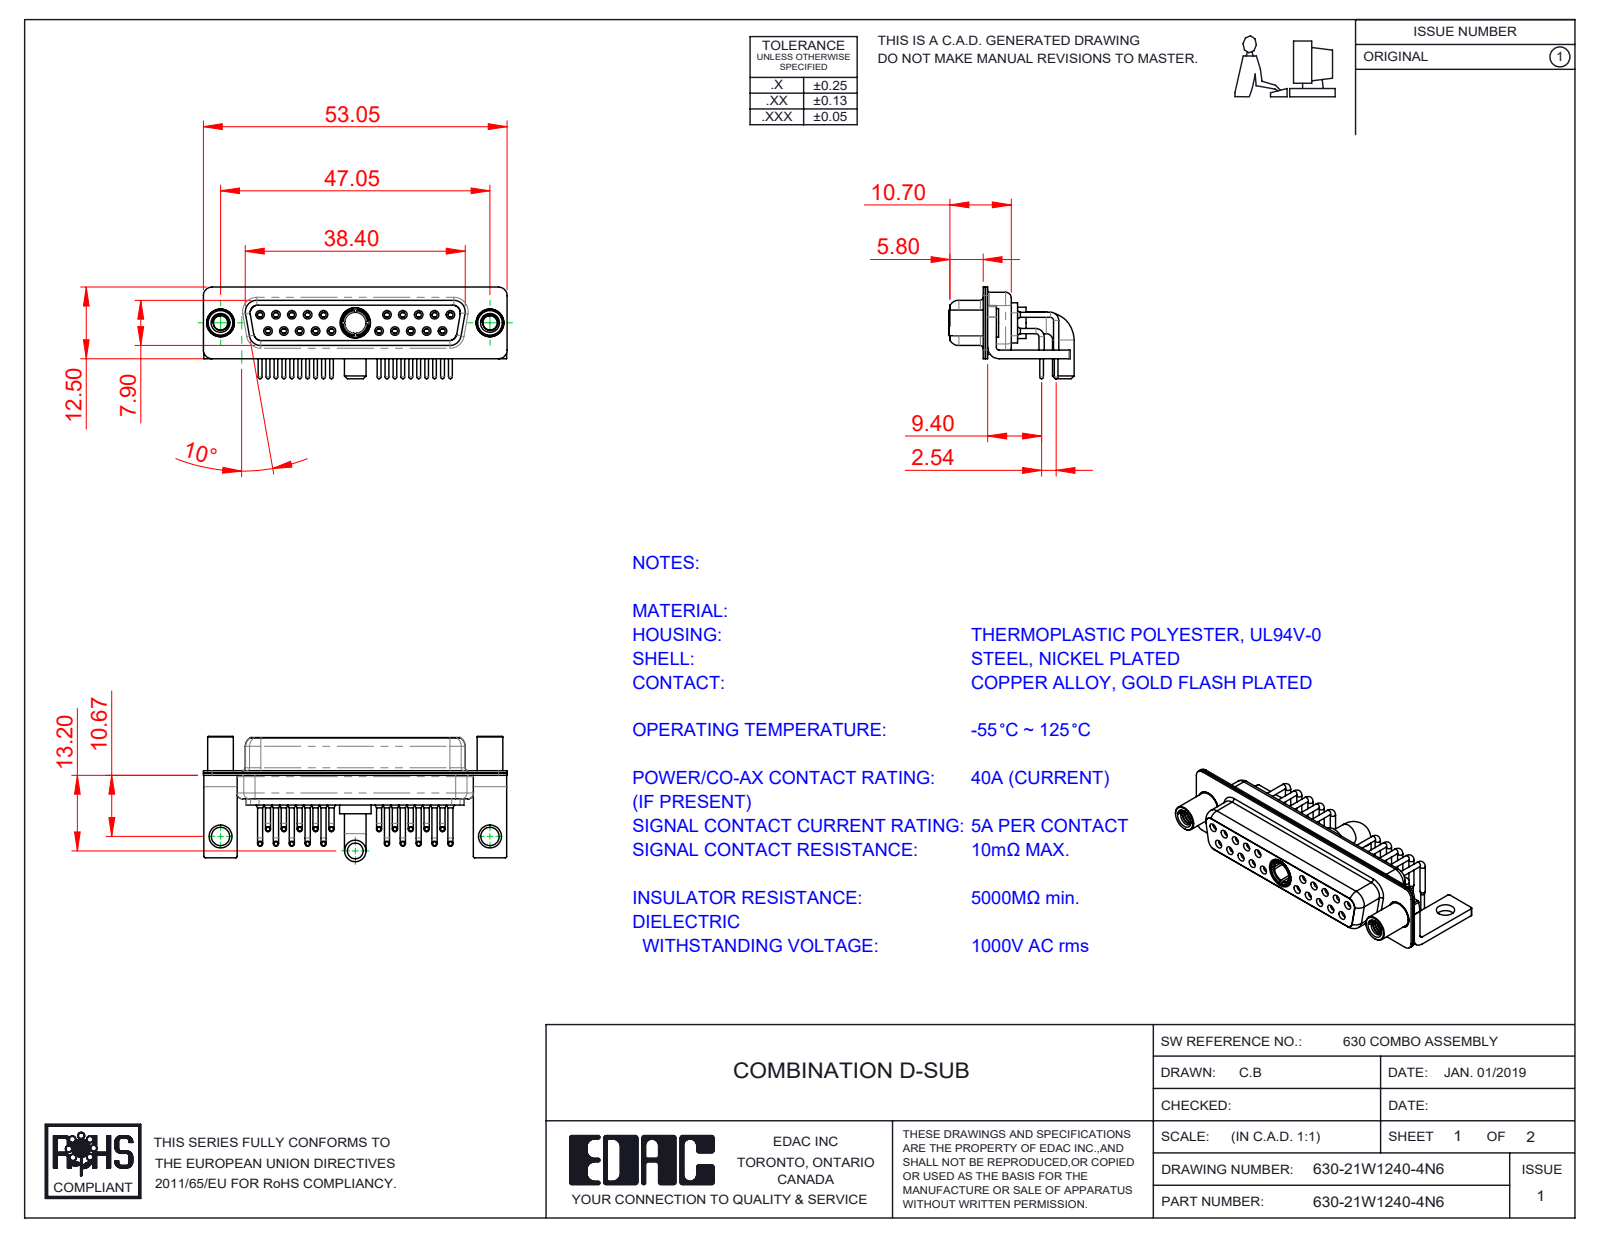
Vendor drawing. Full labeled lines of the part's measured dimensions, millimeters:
Part name (STEP PRODUCT): 630-21W1240-4N6; 630Combo Shell Rear_25 Contacts; 630Combo Contact Row 2; 630Combo Contact Row 1 (+5 more)
STEP written by: SolidWorks 2020 (CONFIG_CONTROL_DESIGN)
Units: millimetres
Bodies: 29 solids, 1515 faces (418 planar, 694 cylindrical, 403 other)
Overall size (bounding box): 53.05 × 21.88 × 16
Volume: 4 483 mm³ · Surface area: 10 319 mm²
Round holes (diameter × count): ⌀0.9 ×20, ⌀1.1 ×20, ⌀1.5 ×20, ⌀2 ×20, ⌀1.6 ×10, ⌀1.7 ×10, ⌀4.85 ×3, ⌀2.5 ×2, ⌀3.2 ×2, ⌀4 ×2, ⌀4.05 ×2, ⌀3.7 ×1
Round bosses / shafts (diameter × count): ⌀0.9 ×20, ⌀0.65 ×20, ⌀1.6 ×10, ⌀5 ×2, ⌀4.95 ×2, ⌀4.8 ×2, ⌀4.5 ×2, ⌀3.75 ×2
Partial cylindrical surfaces — rounded edges, fillets, slot ends (radius × count): R0.25 ×16, R1.5 ×16, R2 ×13, R1.35 ×8, R1.6 ×8, R0.5 ×5, R0.6 ×4, R0.65 ×4
Main face-to-face distances: 0.4, 0.45, 1.4, 8.45, 0.8, 1.8, 8.9, 6.2, 7.05, 1.5
Hole centre spacings: 3.16, 2.77, 5.54, 8.31, 5.04, 19.39, 20.97, 22.16
